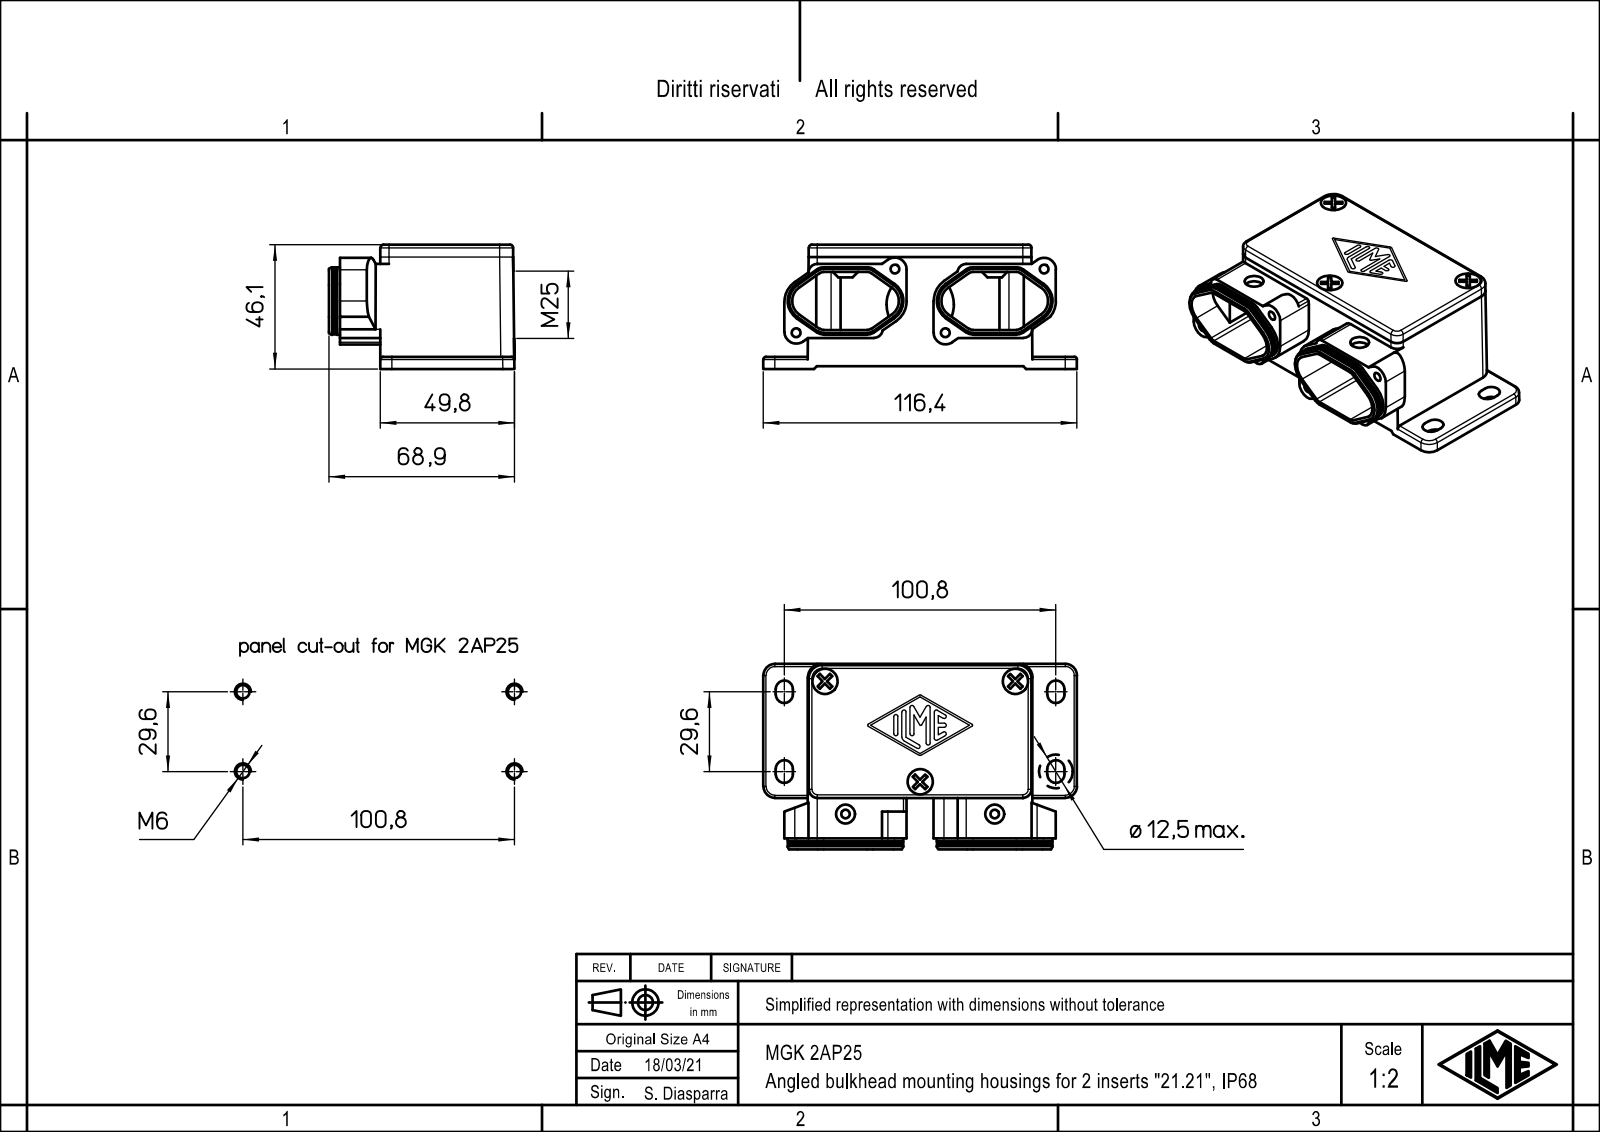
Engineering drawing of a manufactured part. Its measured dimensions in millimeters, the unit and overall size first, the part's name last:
Units: millimetres
Overall size (bounding box): 116.4 × 68.88 × 46.1
Round holes (diameter × count): ⌀3.3 ×4, ⌀3.2 ×2, ⌀7 ×2, ⌀25 ×1
Partial cylindrical surfaces — rounded edges, fillets, slot ends (radius × count): R0.75 ×25, R3.2 ×16, R4.4 ×12, R2.7 ×8, R3.4 ×8, R1 ×5, R1.2 ×4, R4.3 ×4
Main face-to-face distances: 45.1, 4.6, 2.5, 40.5, 38, 42.6, 1, 3.5, 44.96, 41.5
Hole centre spacings: 55.4, 43.63, 13.99, 16.18, 30.11, 47.21, 47.9, 95.08
Volume: 88 258 mm³ · Surface area: 47 695 mm²
Bodies: 1 solid, 469 faces (255 planar, 161 cylindrical, 53 other)
Part name (STEP PRODUCT): MGK_2AP25
STEP written by: Creo Elements/Direct Modeling 20.1B 02-Apr-2019 (C) Parametric Technology GmbH (AUTOMOTIVE_DESIGN)
